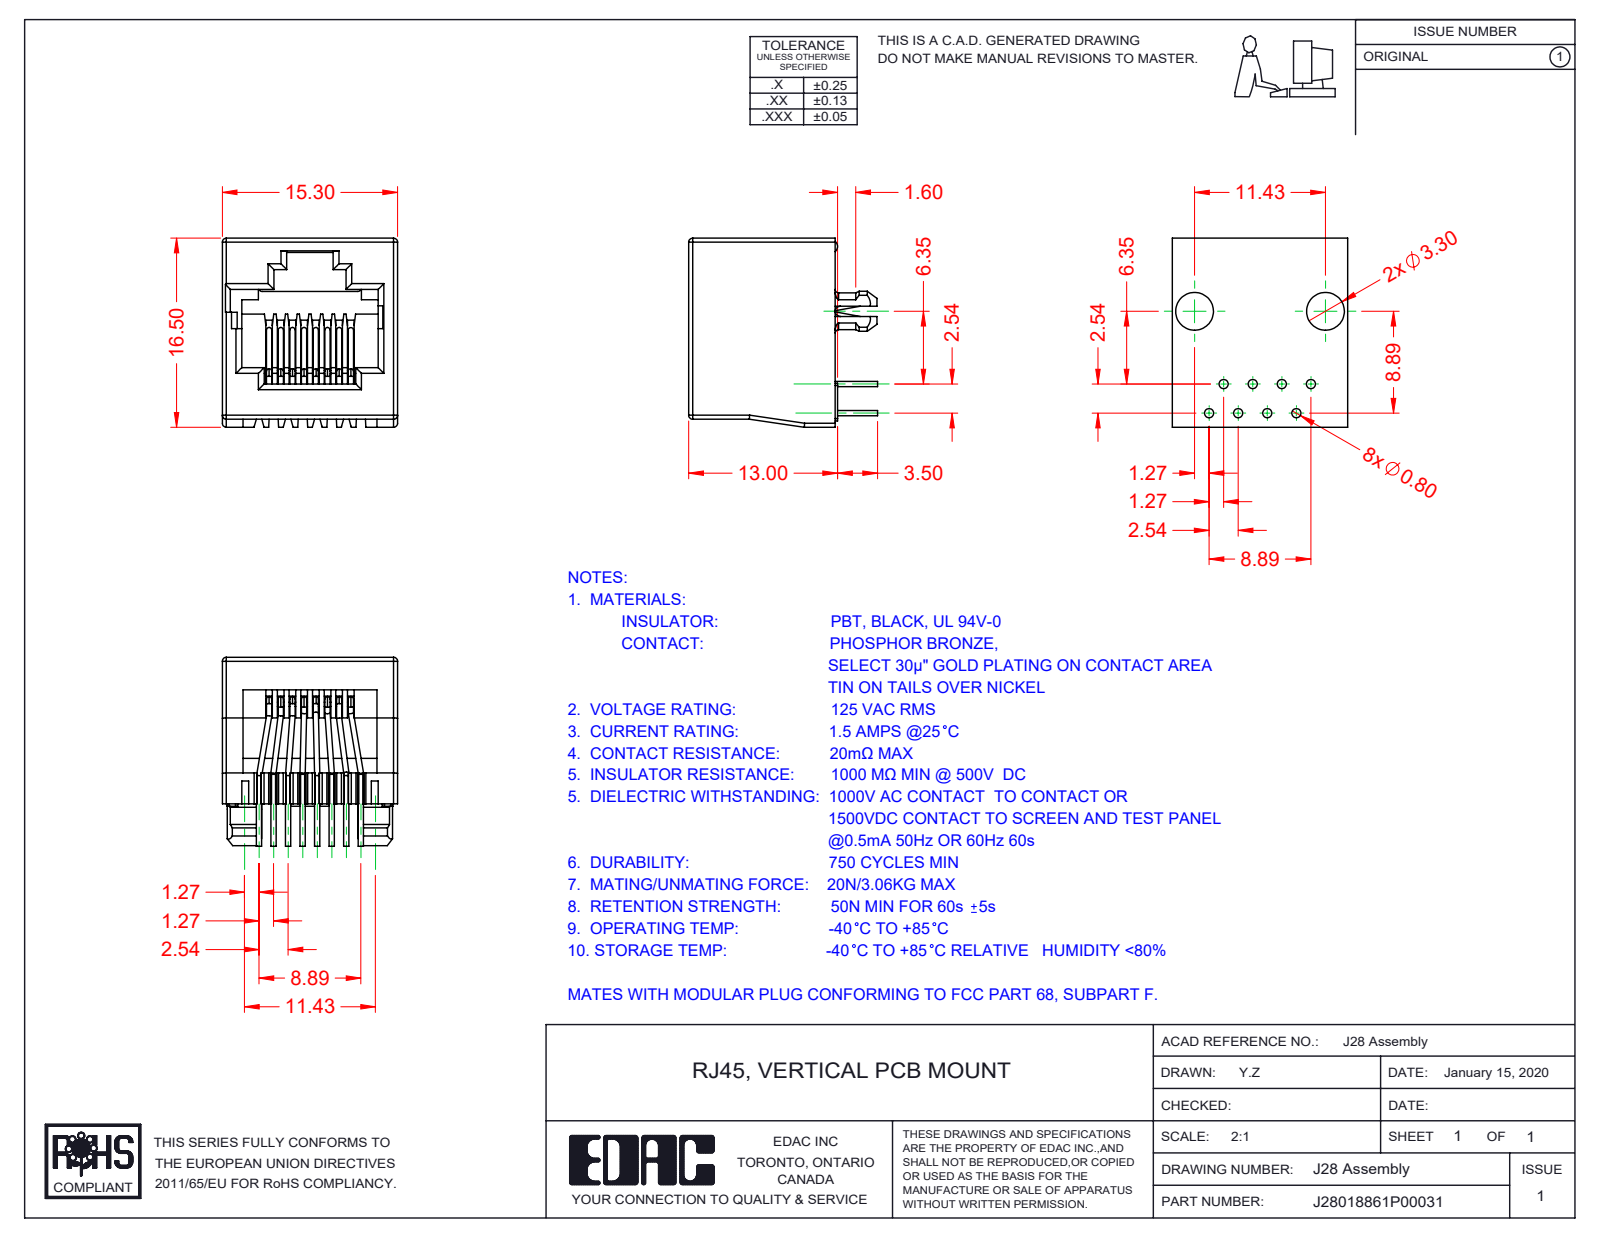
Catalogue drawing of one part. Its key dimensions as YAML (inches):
part_name: "RJ28018861P00031; 28 Contacts; 28 Insulator"
step_written_by: "SolidWorks 2016 (CONFIG_CONTROL_DESIGN)"
units: inches
bodies: {solids: 9, faces: 580, planar: 319, cylindrical: 205, other: 56}
overall_size: [0.65, 0.65, 0.602]
volume: 0.094
surface_area: 4.255
round_holes:
  - {diameter: 0.063, count: 2}
round_bosses_or_shafts:
  - {diameter: 0.018, count: 45}
partial_cylinders:
  - {radius: 0.02, count: 19}
  - {radius: 0.004, count: 16}
  - {radius: 0.014, count: 14}
  - {radius: 0.01, count: 10}
  - {radius: 0.008, count: 8}
  - {radius: 0.009, count: 8}
  - {radius: 0.018, count: 2}
  - {radius: 0.063, count: 2}
face_to_face_distances: [0.602, 0.04, 0.067, 0.535, 0.049, 0.08, 0.504, 0.12, 0.124, 0.478]
hole_center_spacings: [0.472]
